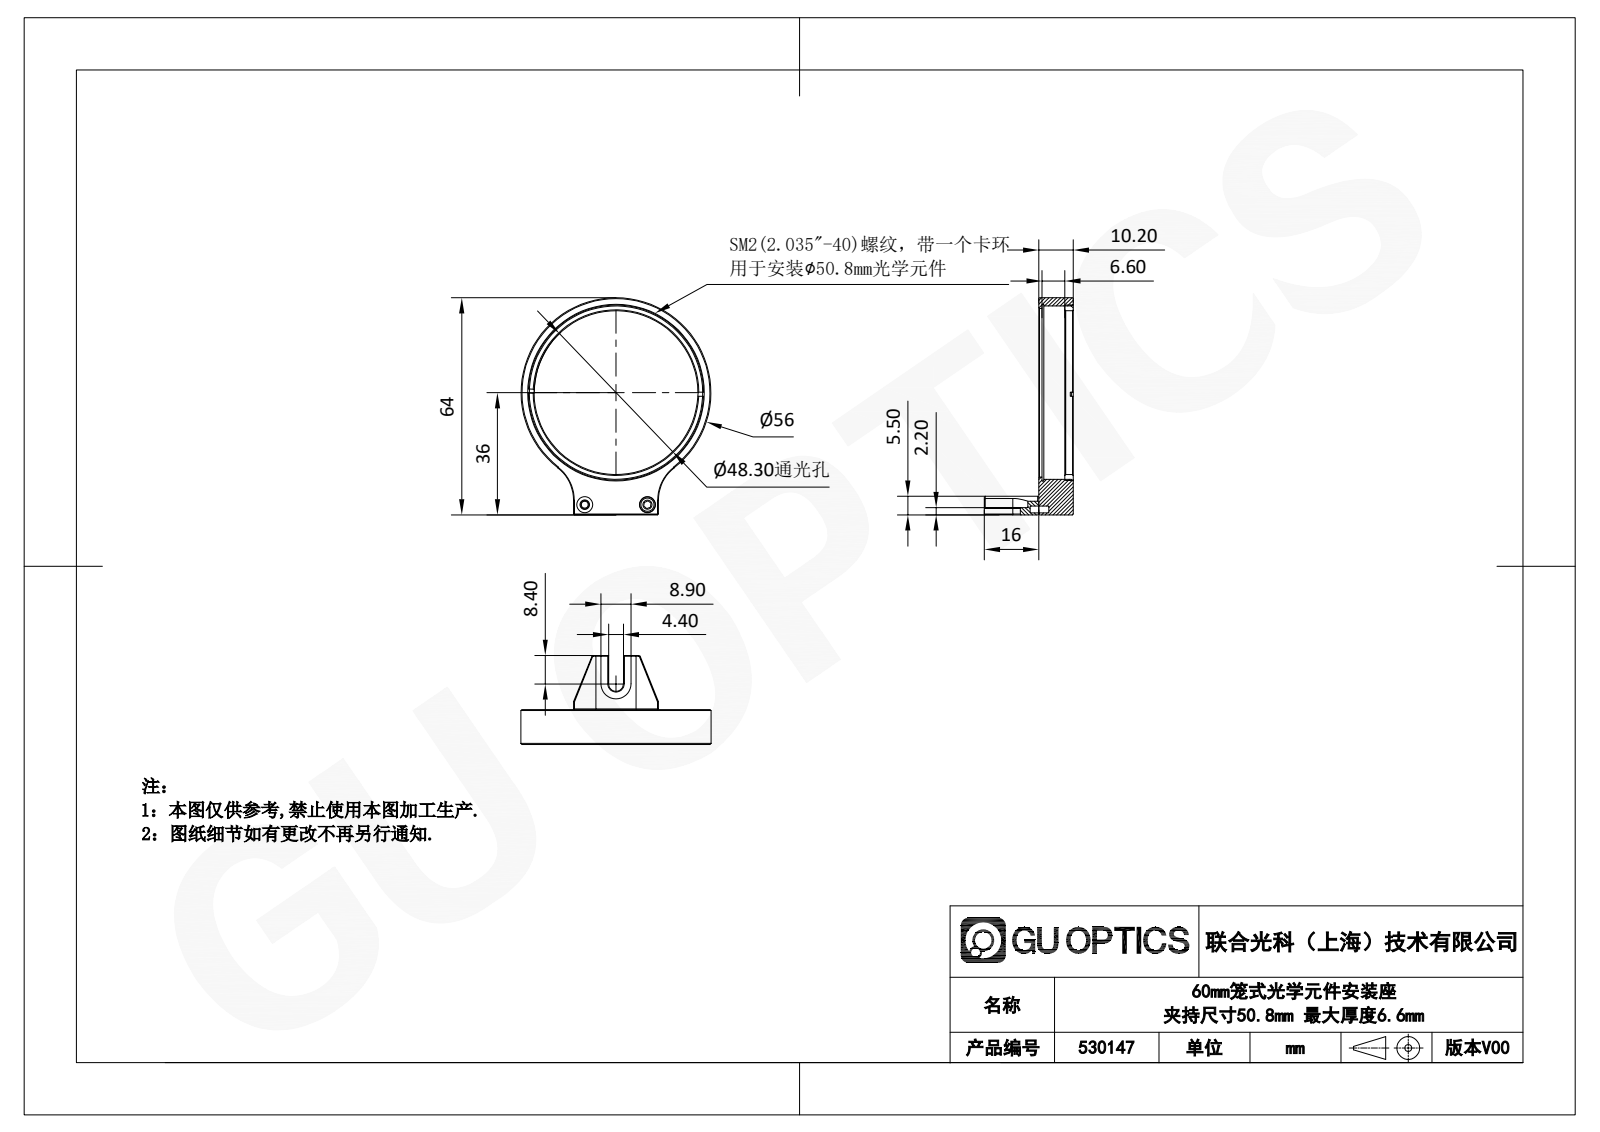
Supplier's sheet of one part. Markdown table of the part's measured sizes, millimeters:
| quantity | value |
| --- | --- |
| part name | 530147 |
| STEP written by | SolidWorks 2020 (CONFIG_CONTROL_DESIGN) |
| units | millimeters |
| bodies | 0 solids, 114 faces (82 planar, 12 cylindrical, 20 other) |
| overall size | 64 × 56 × 26.2 |
| round holes (diameter × count) | 4.8 × 2, 49.69 × 1, 51.09 × 1, 52.09 × 1 |
| round bosses / shafts (diameter × count) | 48.3 × 1 |
| partial cylindrical surfaces (radius × count) | 12 × 2, 2.2 × 1, 4.45 × 1, 12.5 × 1, 28 × 1 |
| main face-to-face distances | 10.2, 1, 9.2, 7.7, 6.7, 2.5, 5.5, 0.5, 6.2, 1.5 |
| hole center spacings | 34.27, 18.5 |
